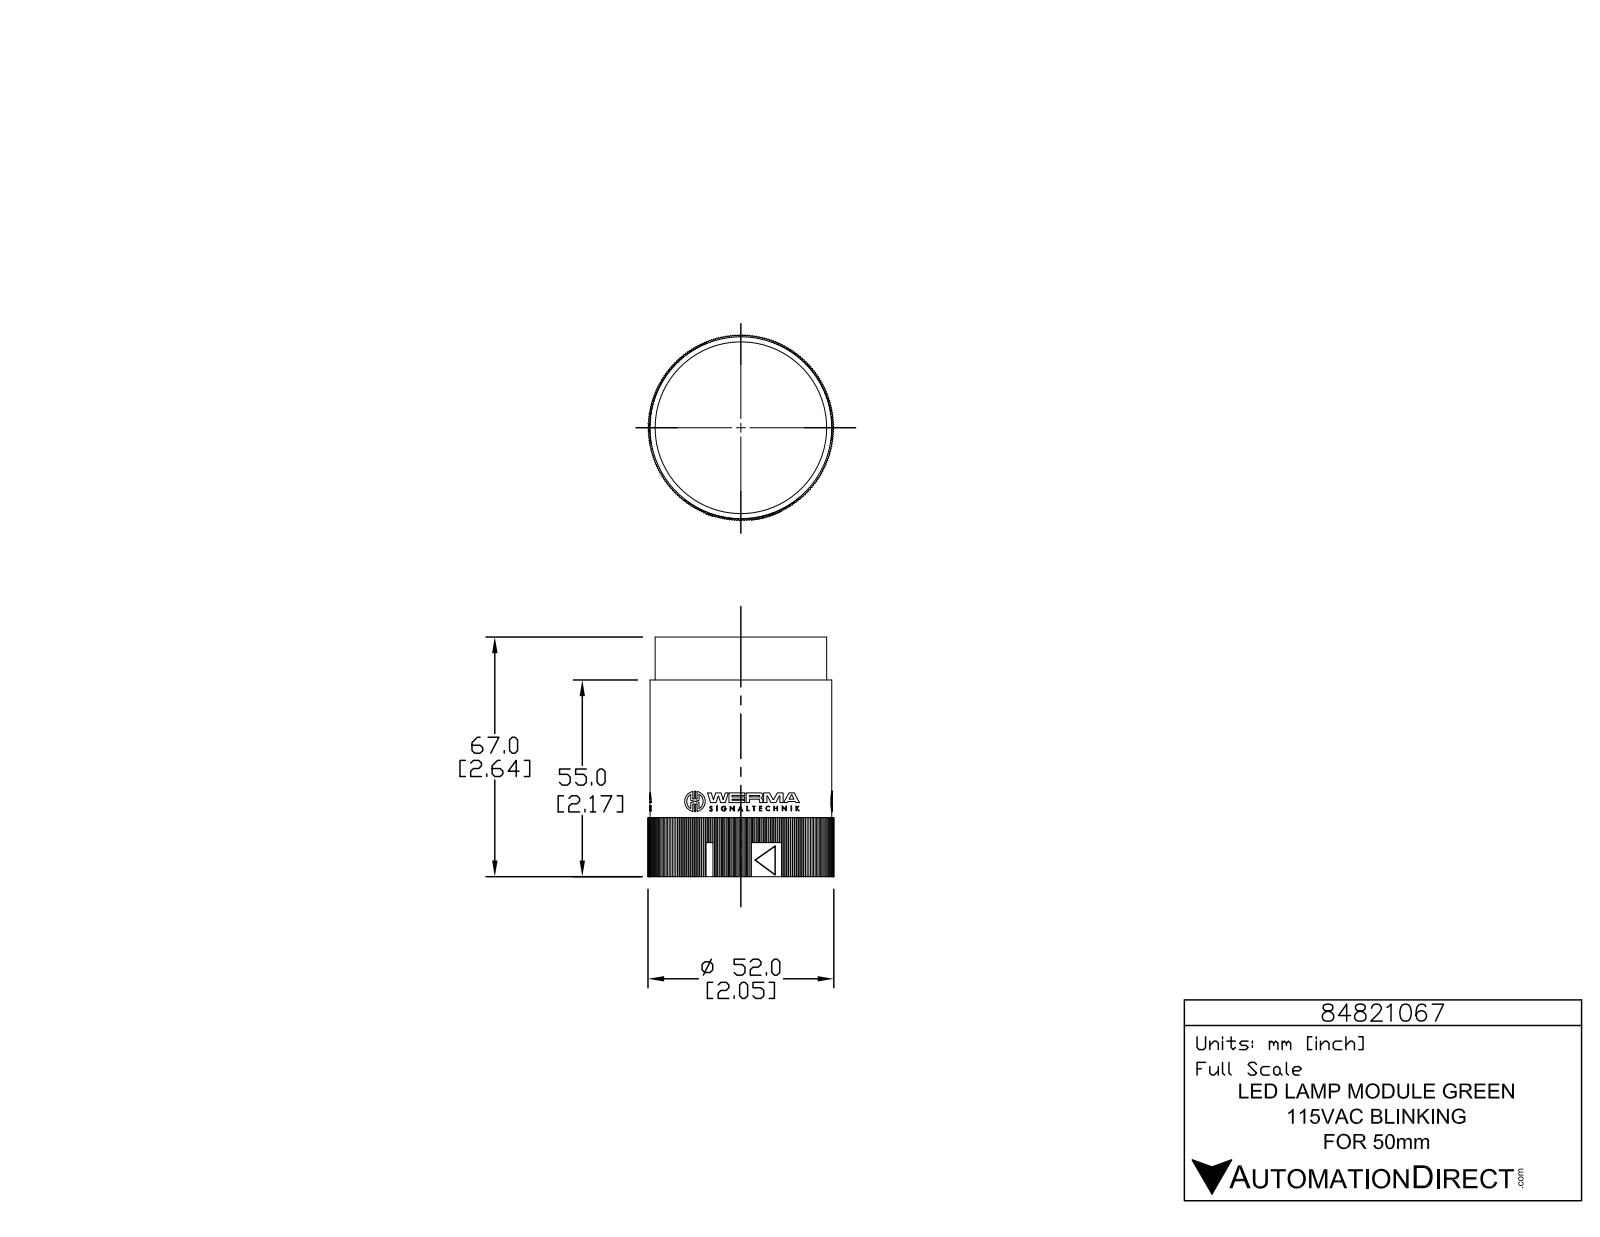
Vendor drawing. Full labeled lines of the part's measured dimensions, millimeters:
Part name (STEP PRODUCT): 84821067
STEP written by: SolidWorks 2015 (AUTOMOTIVE_DESIGN)
Units: millimetres
Bodies: 1 solid, 1265 faces (1020 planar, 245 cylindrical, 0 other)
Overall size (bounding box): 67 × 52 × 52
Volume: 112 600 mm³ · Surface area: 17 820 mm²
Round holes (diameter × count): ⌀1 ×3, ⌀48.2 ×1
Round bosses / shafts (diameter × count): ⌀5.7 ×3, ⌀1.4 ×3, ⌀50.9 ×1, ⌀48 ×1
Partial cylindrical surfaces — rounded edges, fillets, slot ends (radius × count): R0.2 ×6, R0.2 ×6, R0.2 ×6, R3.3 ×6, R0.1 ×3, R0.1 ×3, R0.2 ×3, R0.2 ×3
Main face-to-face distances: 55, 36.3, 36.3, 36.3, 12, 67, 36.3, 36.3, 43, 50.5
